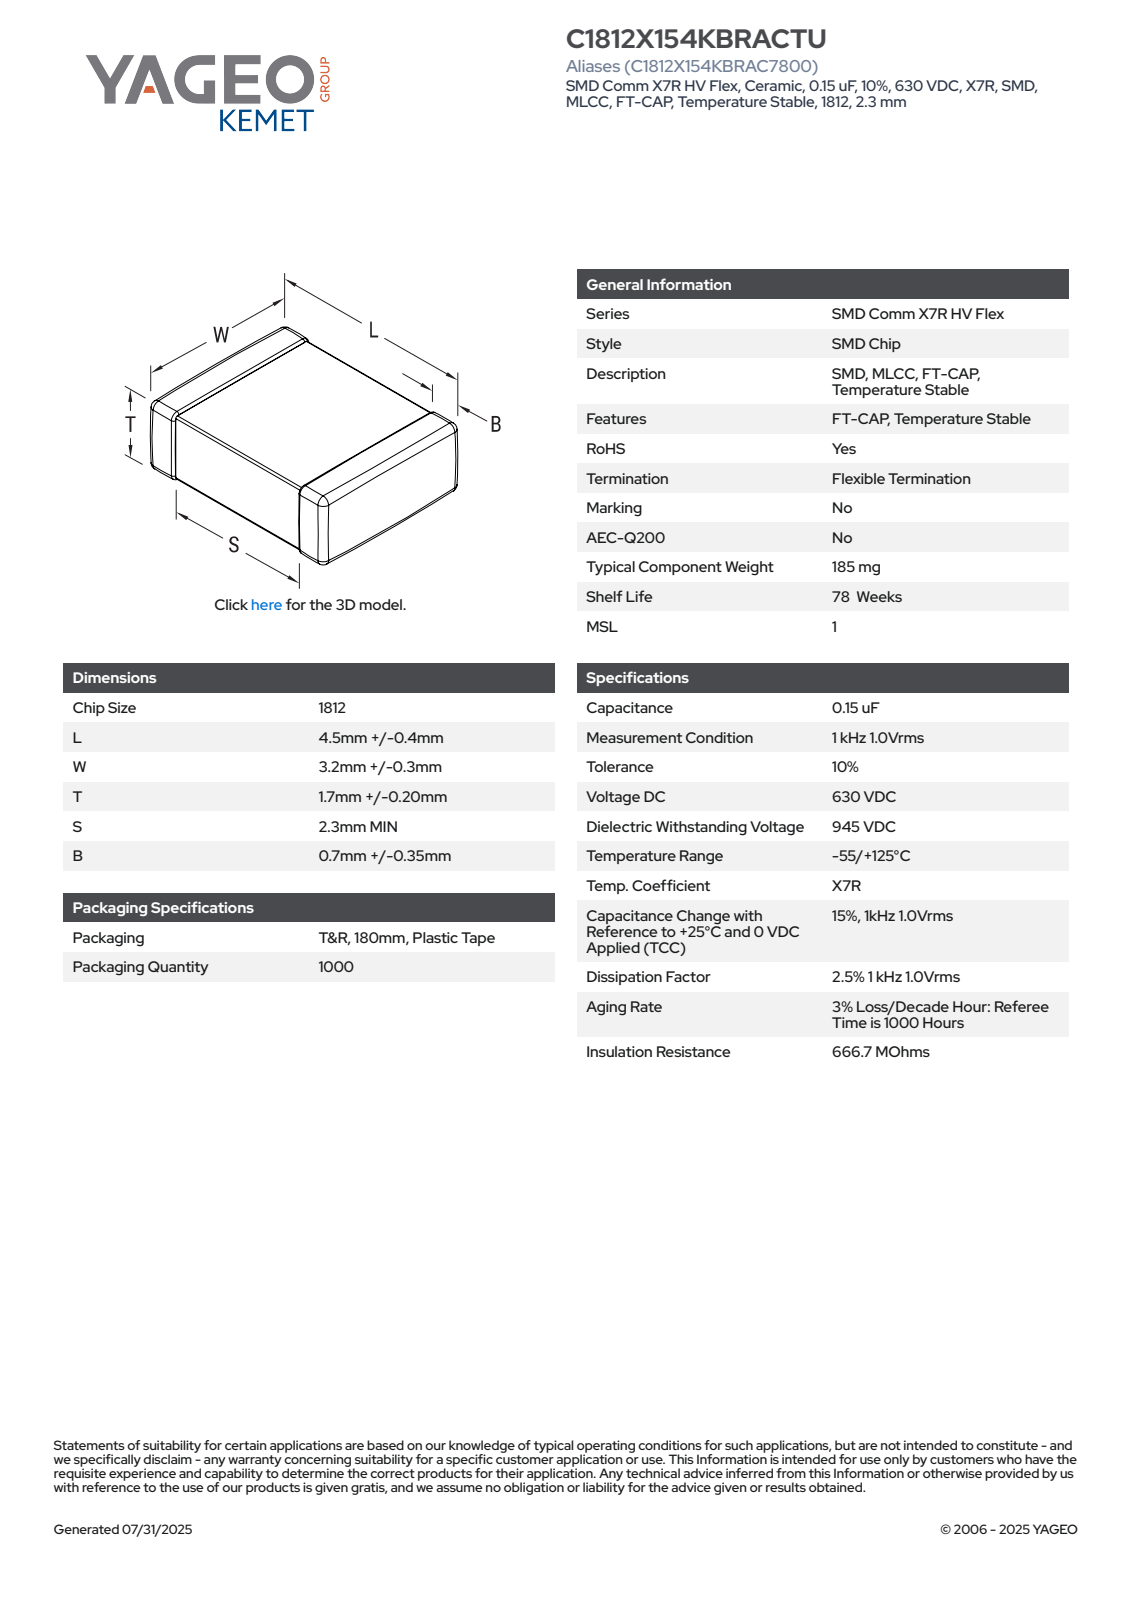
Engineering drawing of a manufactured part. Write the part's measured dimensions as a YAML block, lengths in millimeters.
part_name: "CCS_CCSTDNOS_1812_L4.9W3.5T1.9B1.05"
step_written_by: "SolidWorks 2014 (AUTOMOTIVE_DESIGN)"
units: millimeters
bodies: {solids: 4, faces: 125, planar: 71, cylindrical: 38, other: 16}
overall_size: [4.9, 3.5, 1.9]
volume: 30
surface_area: 65
face_to_face_distances: [1.83, 1.76, 3.43, 1.9, 4.9, 3.36, 3.5, 1.42, 1.94, 1.49]
